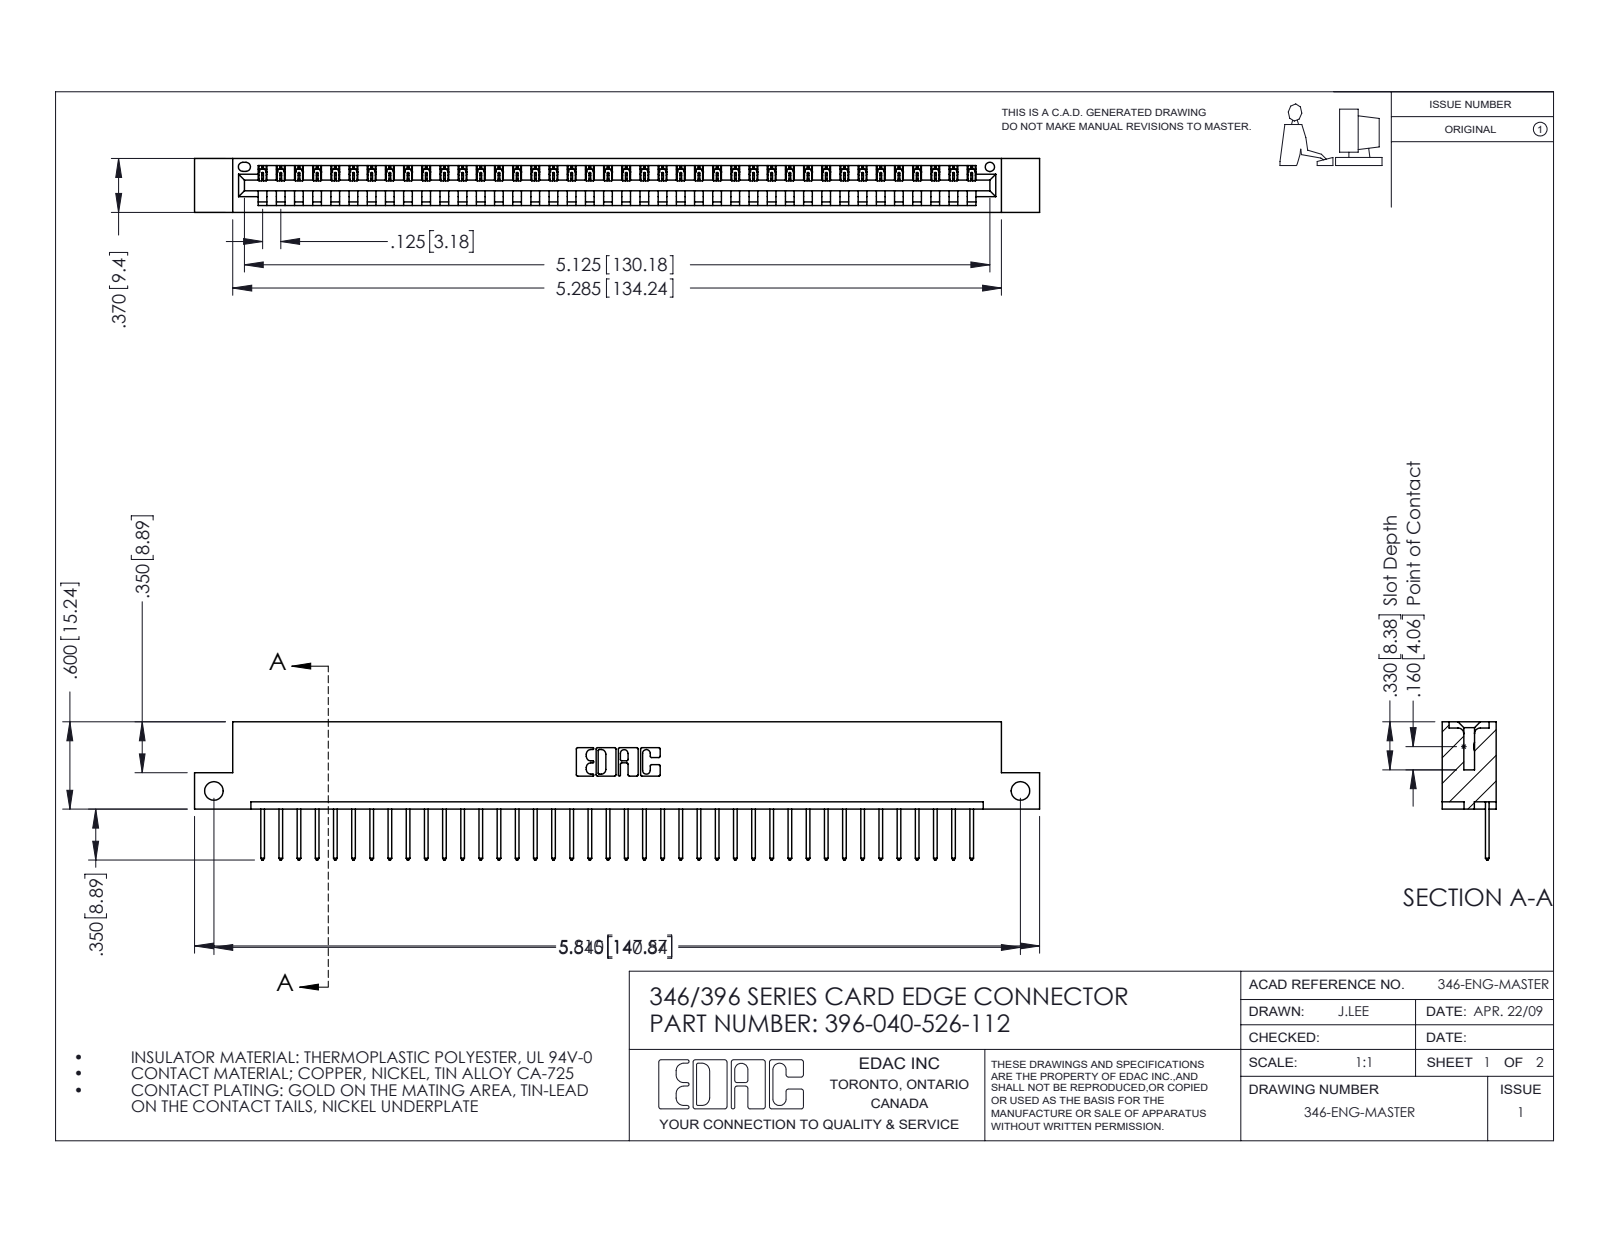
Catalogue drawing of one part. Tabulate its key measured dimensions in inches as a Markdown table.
| quantity | value |
| --- | --- |
| part name | 346 Part_Flush Mounting Lugs - Side Mount; 345-292-001_345-293-126; 396-040-526-112 |
| STEP written by | SolidWorks 2016 (CONFIG_CONTROL_DESIGN) |
| units | inches |
| bodies | 41 solids, 2442 faces (1676 planar, 766 cylindrical, 0 other) |
| overall size | 5.81 × 0.95 × 0.37 |
| volume | 0.854 in³ |
| surface area | 26.79 in² |
| round holes (diameter × count) | 0.128 × 2, 0.064 × 1 |
| partial cylindrical surfaces (radius × count) | 0.006 × 80, 0.01 × 80, 0.01 × 22, 0.007 × 6, 0.031 × 6, 0.026 × 3, 0.031 × 2, 0.04 × 2 |
| main face-to-face distances | 0.048, 0.322, 0.37, 0.25, 0.072, 0.298, 0.025, 0.148, 0.222, 0.1 |
| hole center spacings | 5.545 |
